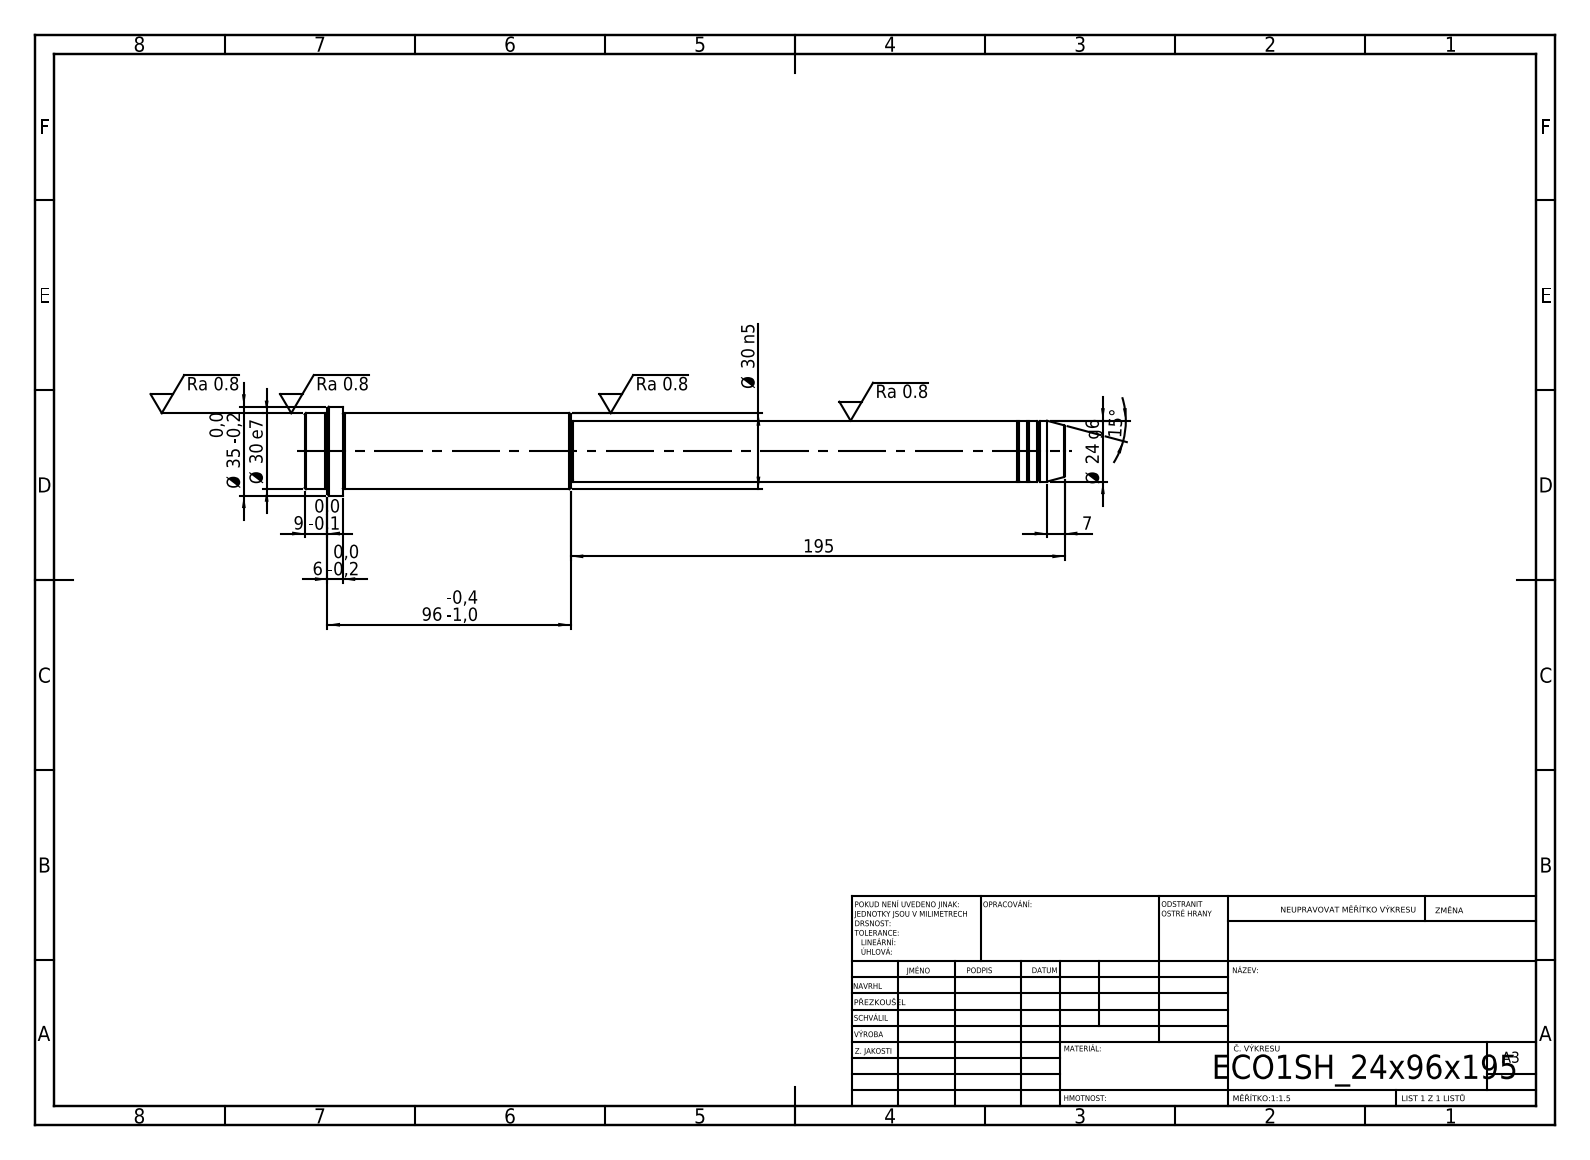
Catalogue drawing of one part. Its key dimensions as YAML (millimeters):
step_written_by: "SolidWorks 2019 (CONFIG_CONTROL_DESIGN)"
units: millimeters
bodies: {solids: 1, faces: 52, planar: 6, cylindrical: 16, other: 30}
overall_size: [300, 35, 35]
volume: 163263
surface_area: 26659
round_bosses_or_shafts:
  - {diameter: 35, count: 1}
  - {diameter: 30, count: 1}
  - {diameter: 24, count: 1}
  - {diameter: 23, count: 1}
face_to_face_distances: [300, 285, 15, 195, 90, 105, 291, 96, 6, 9]
